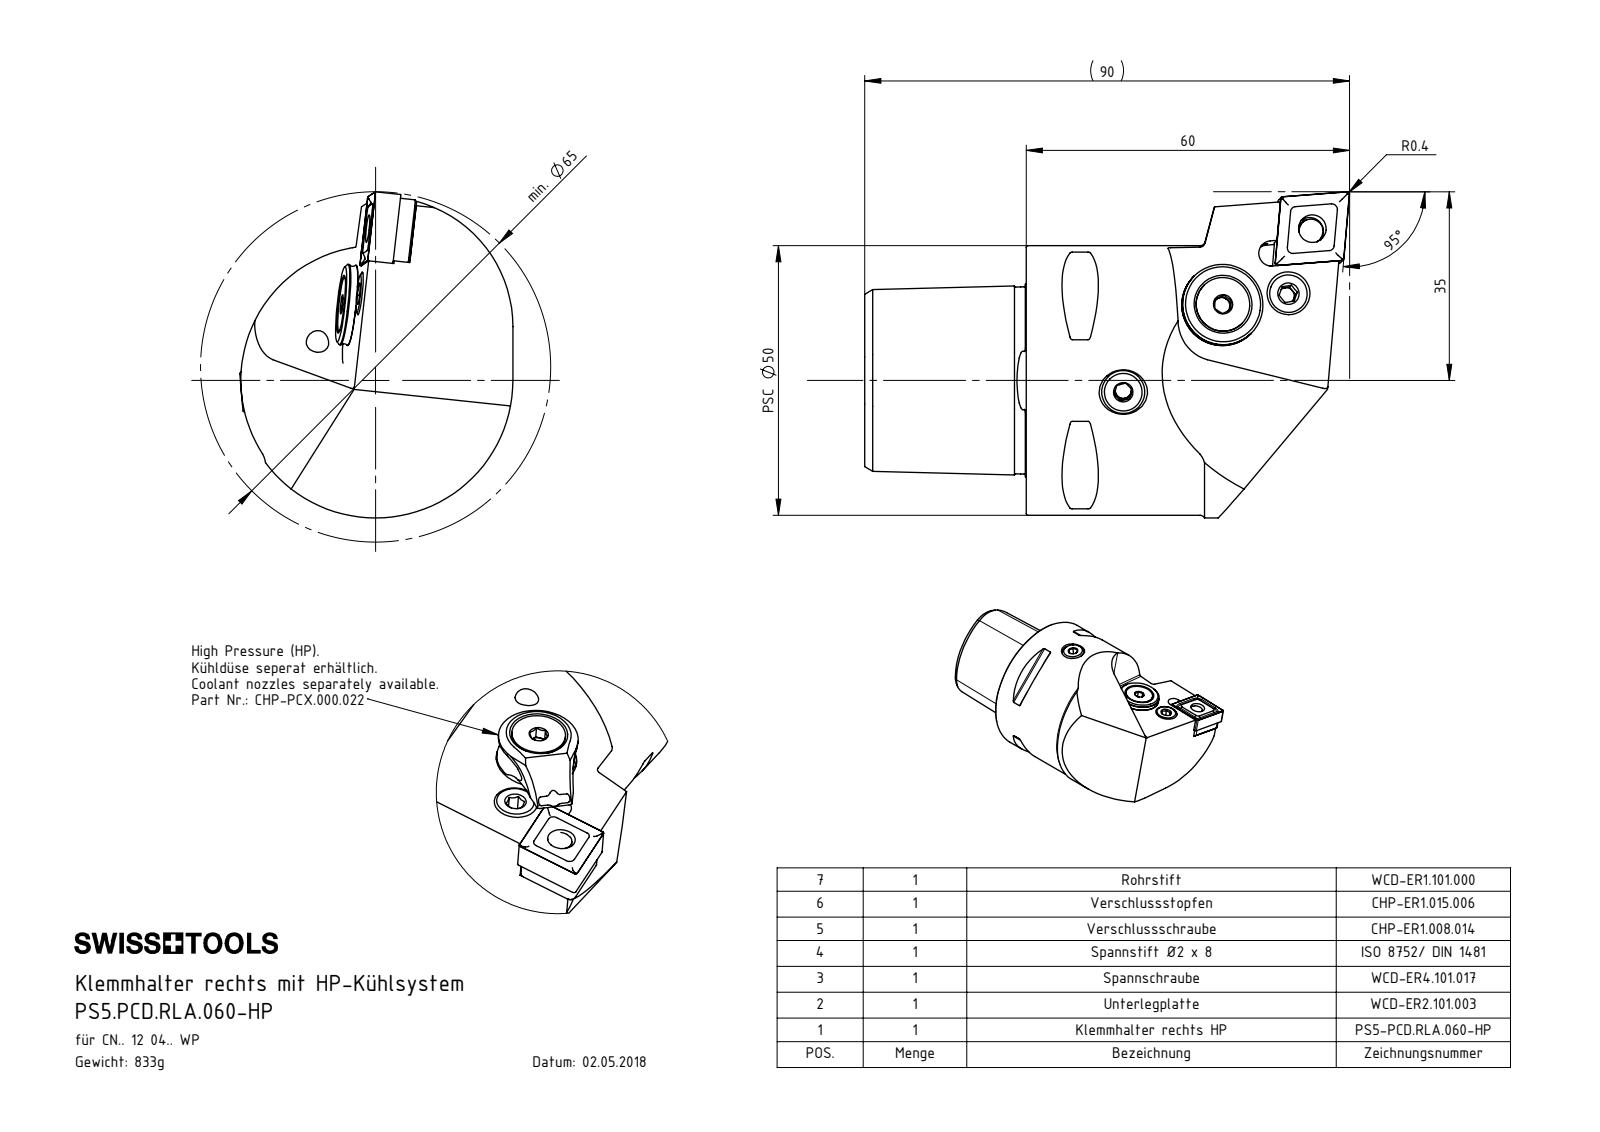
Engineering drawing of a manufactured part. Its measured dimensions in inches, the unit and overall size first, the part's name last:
Units: inches
Overall size (bounding box): 3.543 × 2.363 × 1.988
Round holes (diameter × count): ⌀0.165 ×3, ⌀0.197 ×2, ⌀0.276 ×2, ⌀0.047 ×1, ⌀0.079 ×1, ⌀0.098 ×1, ⌀0.118 ×1, ⌀0.157 ×1, ⌀0.203 ×1, ⌀0.205 ×1, ⌀0.24 ×1, ⌀0.252 ×1
Round bosses / shafts (diameter × count): ⌀0.315 ×2, ⌀1.969 ×1, ⌀0.591 ×1, ⌀0.528 ×1, ⌀0.394 ×1, ⌀0.311 ×1, ⌀0.252 ×1, ⌀0.217 ×1
Partial cylindrical surfaces — rounded edges, fillets, slot ends (radius × count): R0.02 ×8, R0.016 ×4, R0.039 ×4, R0.098 ×2, R0.083 ×1, R0.087 ×1, R0.093 ×1, R0.114 ×1
Main face-to-face distances: 1.181, 0.177, 0.176, 0.755, 0.124, 0.125, 0.301, 1.748, 0.46, 0.787
Hole centre spacings: 0.177, 0.411, 0.481, 0.789, 0.791, 0.928, 0.504, 0.506
Volume: 6.483 in³ · Surface area: 37.81 in²
Bodies: 10 solids, 319 faces (130 planar, 69 cylindrical, 120 other)
Part name (STEP PRODUCT): CNMG120404; WCD; WCD-ER3.101.000_A; DIN 7991 - M5x15 (+8 more)
STEP written by: SolidWorks 2017 (AUTOMOTIVE_DESIGN)
